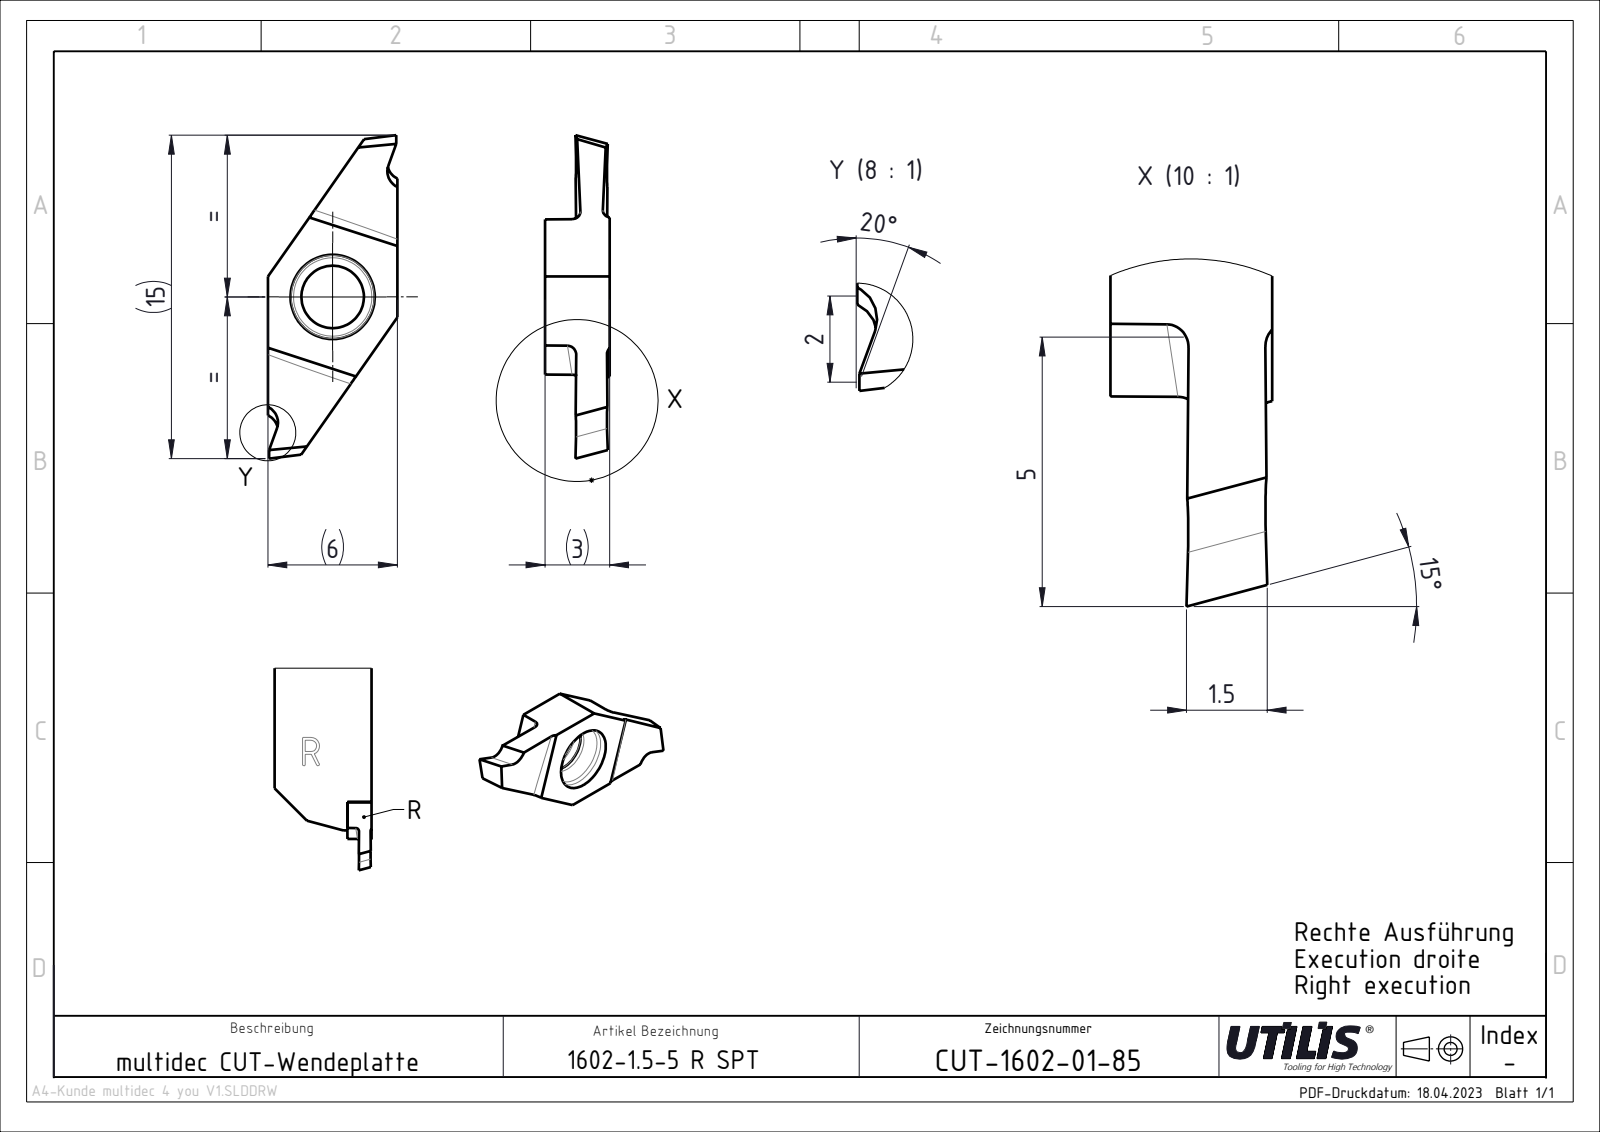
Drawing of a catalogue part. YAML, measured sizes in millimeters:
part_name: "1-CUT-1602-01-85 stp"
step_written_by: "SolidWorks 2022 (AUTOMOTIVE_DESIGN)"
units: millimeters
bodies: {solids: 1, faces: 19, planar: 14, cylindrical: 5, other: 0}
overall_size: [15, 6, 3]
volume: 118
surface_area: 216
round_holes:
  - {diameter: 2.9, count: 1}
partial_cylinders:
  - {radius: 0.4, count: 4}
face_to_face_distances: [6, 3, 1.35]
